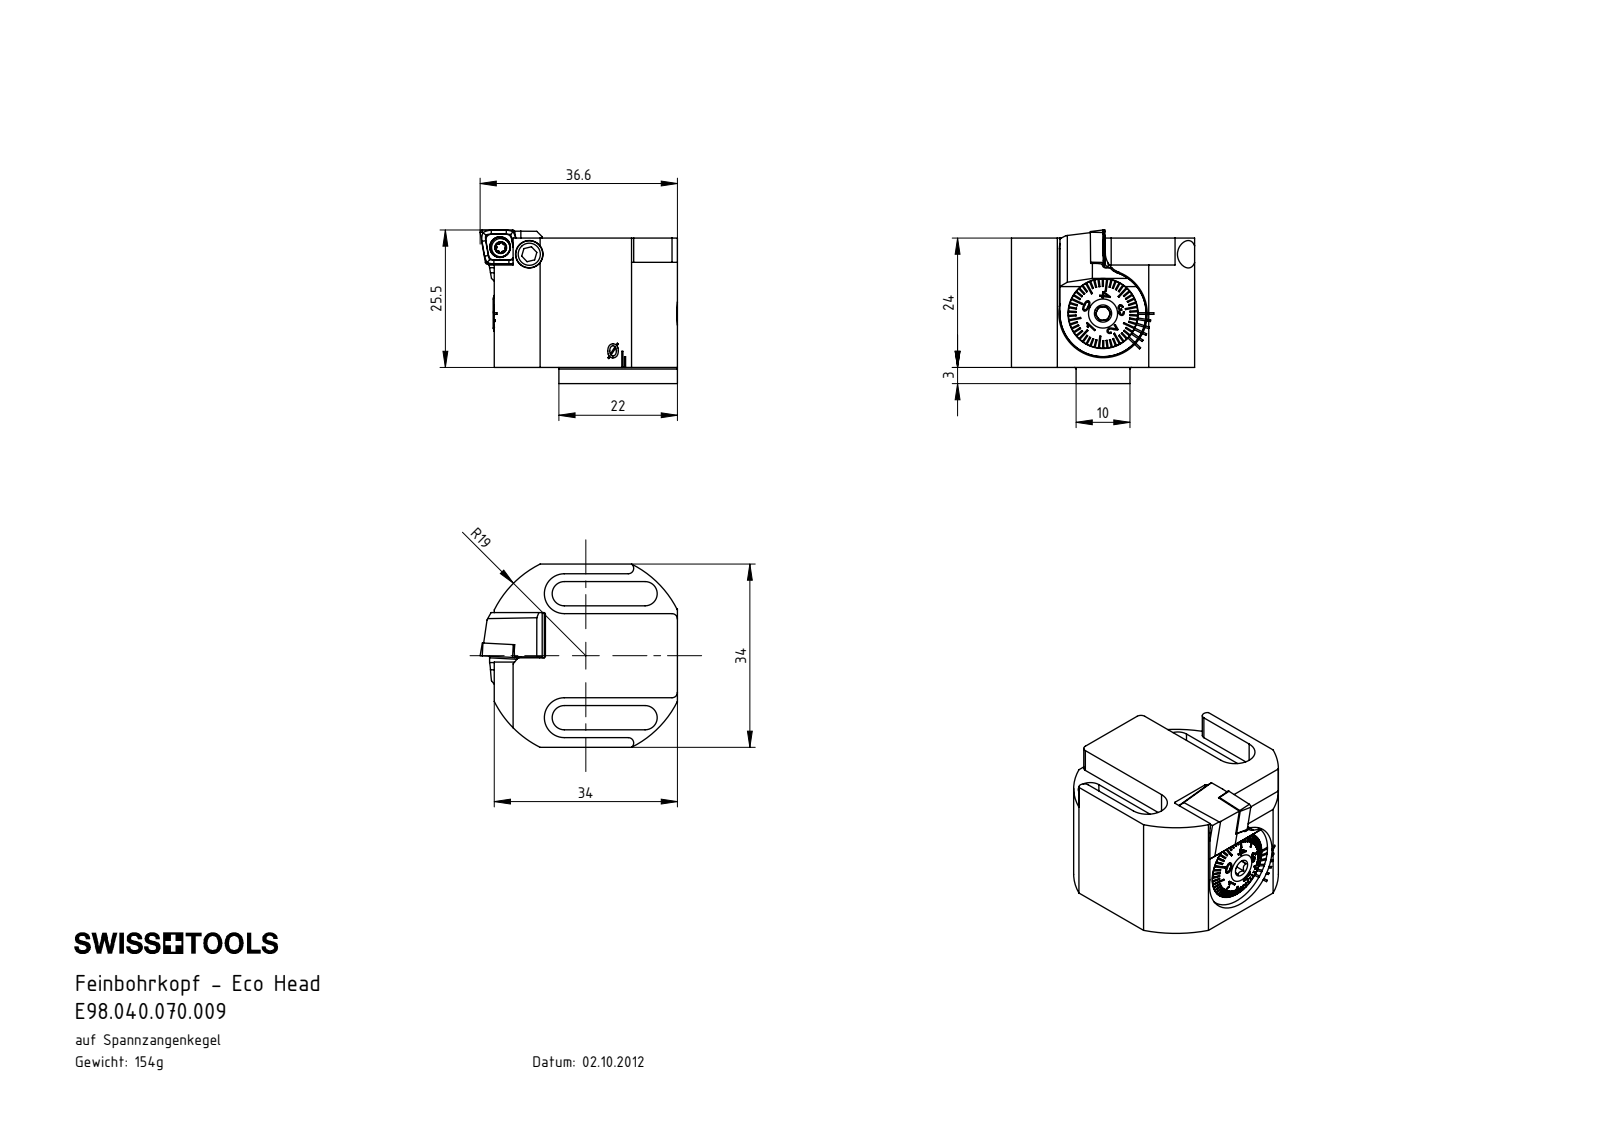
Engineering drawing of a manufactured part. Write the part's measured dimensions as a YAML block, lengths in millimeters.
part_name: "ISO 4026 - M5 x 10_ISO 4026 - M5 x 10; Exx-EH1.038.023_B; ISO 2338 - 2 h8 x 10; DIN 5401-03 (+8 more)"
step_written_by: "SolidWorks 2017 (AUTOMOTIVE_DESIGN)"
units: millimeters
bodies: {solids: 26, faces: 617, planar: 325, cylindrical: 89, other: 203}
overall_size: [36.62, 34, 28.5]
volume: 20094
surface_area: 16081
round_holes:
  - {diameter: 2, count: 1}
  - {diameter: 2.05, count: 1}
  - {diameter: 2.5, count: 1}
  - {diameter: 2.8, count: 1}
  - {diameter: 3.85, count: 1}
  - {diameter: 4.2, count: 1}
  - {diameter: 5.1, count: 1}
  - {diameter: 6, count: 1}
  - {diameter: 6.4, count: 1}
  - {diameter: 7, count: 1}
  - {diameter: 7.5, count: 1}
  - {diameter: 8.2, count: 1}
round_bosses_or_shafts:
  - {diameter: 17.4, count: 1}
  - {diameter: 16.4, count: 1}
  - {diameter: 16.34, count: 1}
  - {diameter: 16, count: 1}
  - {diameter: 13.1, count: 1}
  - {diameter: 12.85, count: 1}
  - {diameter: 11.2, count: 1}
  - {diameter: 6.9, count: 1}
partial_cylinders:
  - {radius: 0.21, count: 6}
  - {radius: 0.3, count: 5}
  - {radius: 0.36, count: 5}
  - {radius: 1, count: 4}
  - {radius: 2.25, count: 4}
  - {radius: 0.5, count: 2}
  - {radius: 3.7, count: 2}
  - {radius: 0.36, count: 1}
face_to_face_distances: [4.5, 23, 24, 3.25, 7.75, 26.25, 30.75, 34, 3, 18.5]
